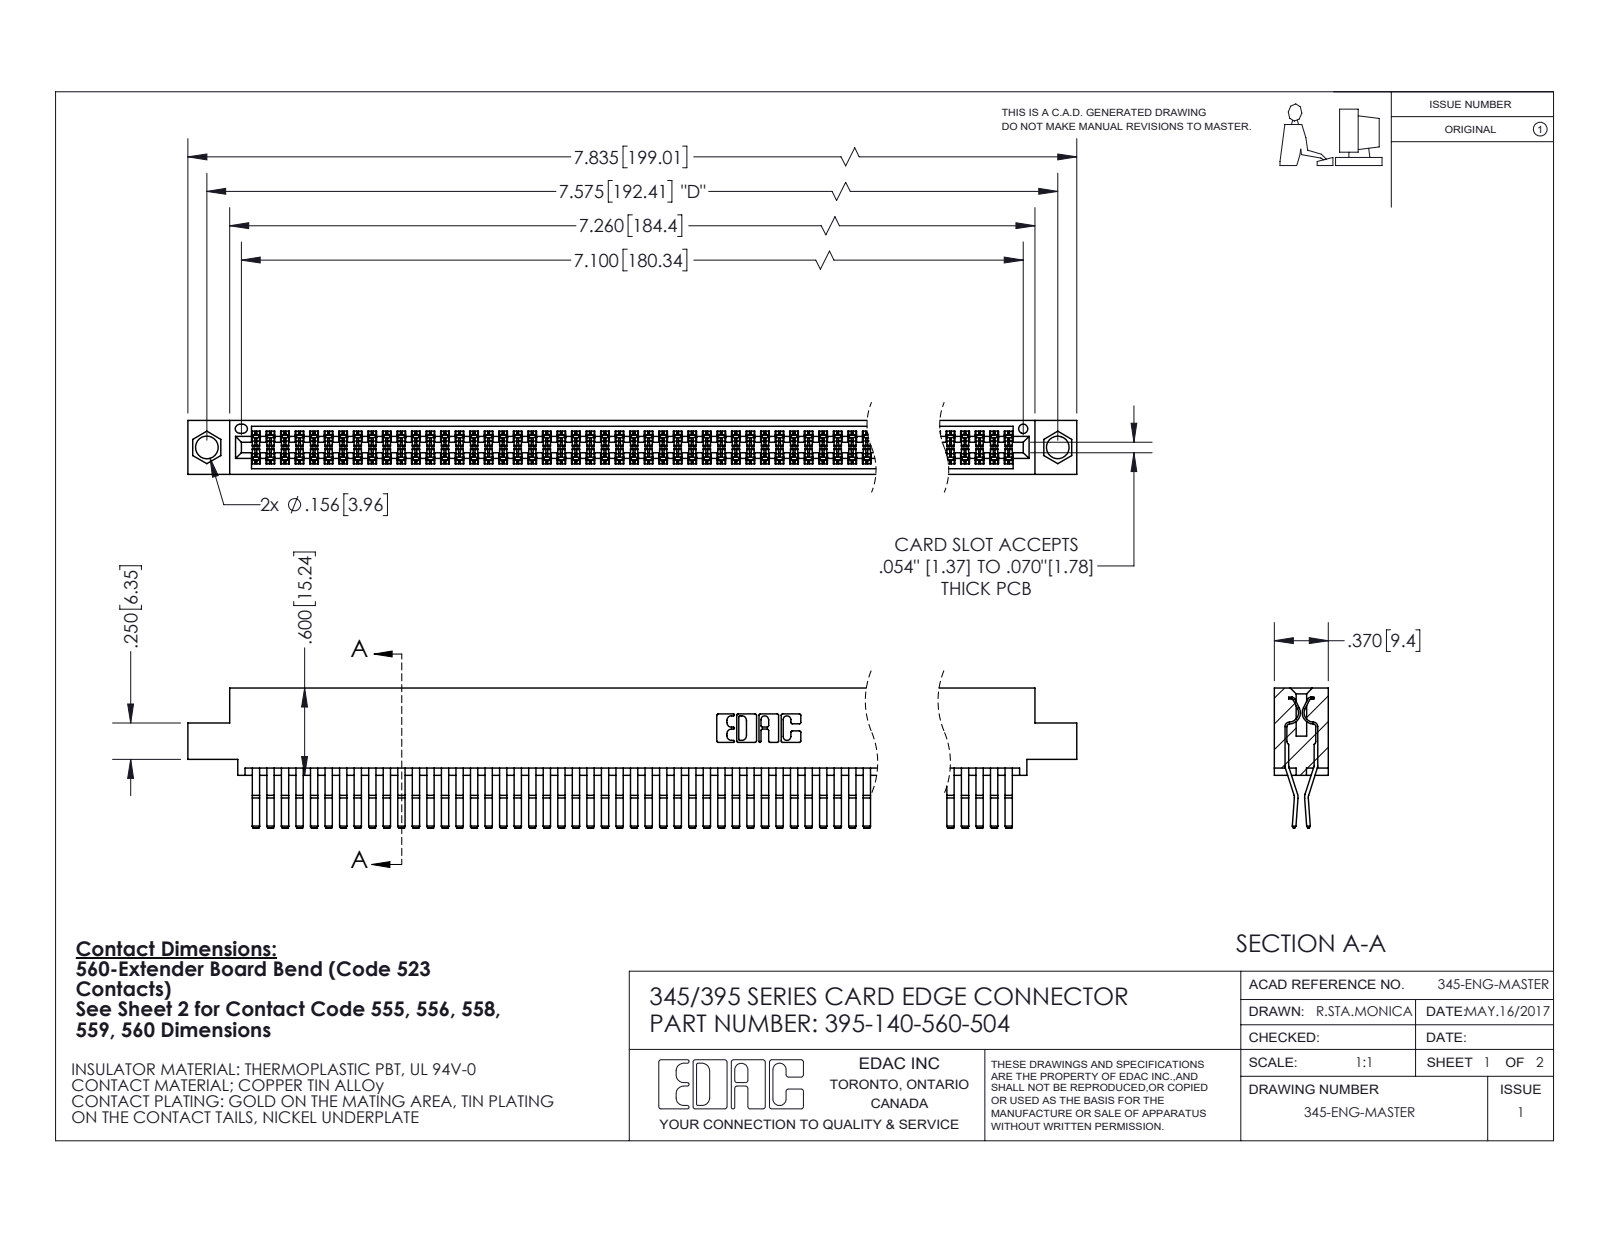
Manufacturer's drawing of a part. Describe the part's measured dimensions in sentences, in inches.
The part is named "395-140-560-504; 345-292-001_560 Tail; 345 Part_0.110 Offset - 0.156 Dia-TI". Its 3-D file was written by "SolidWorks 2020 (CONFIG_CONTROL_DESIGN)". It is 141 solids with 7424 faces: 4718 planar, 2706 cylindrical and 0 other. Overall it measures 7.835 by 0.962 by 0.37 inches. Its volume is 1.241 cubic inches and its surface area 50.99 square inches. Round holes: 2 of diameter 0.156, 1 of diameter 0.064. Partial cylindrical surfaces (rounded edges, fillets, slot ends): 210 of radius 0.006, 22 of radius 0.01, 6 of radius 0.007, 6 of radius 0.031, 3 of radius 0.026, 2 of radius 0.01, 2 of radius 0.014, 2 of radius 0.019. The main face-to-face distances are 0.025, 0.298, 0.072, 0.37, 0.2, 0.098, 0.272, 0.225, 0.175, 0.149. The hole center spacings are 0.27, 7.339, 7.575.
